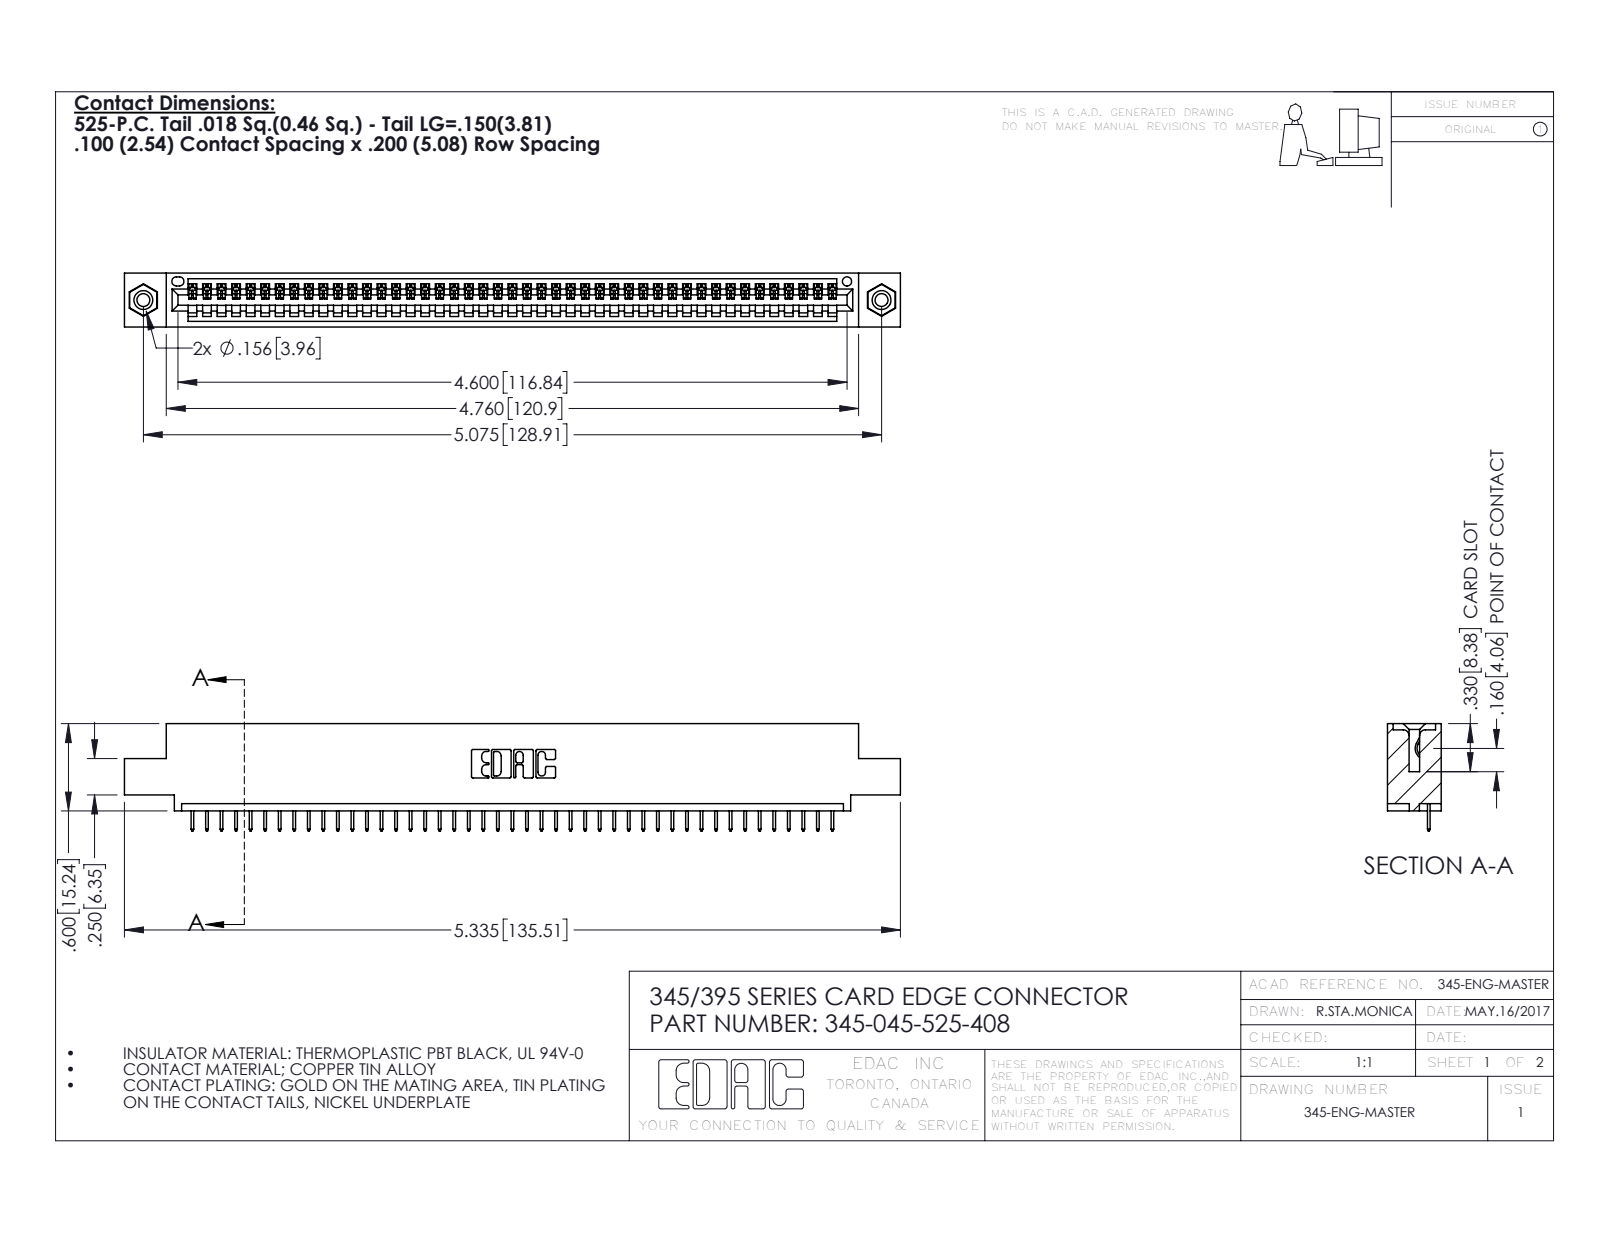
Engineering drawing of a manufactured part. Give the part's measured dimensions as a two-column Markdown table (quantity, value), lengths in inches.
| quantity | value |
| --- | --- |
| part name | 345-250-001_345-250-003-102; 345-292-001_345-293-125; 345 Part_0.110 Offset - 0.156 Dia-TI; 345-045-525-408 |
| STEP written by | SolidWorks 2020 (CONFIG_CONTROL_DESIGN) |
| units | inches |
| bodies | 48 solids, 2980 faces (2186 planar, 778 cylindrical, 16 other) |
| overall size | 5.335 × 0.737 × 0.37 |
| volume | 0.771 in³ |
| surface area | 25.29 in² |
| round holes (diameter × count) | 0.089 × 2, 0.125 × 2, 0.156 × 2, 0.064 × 1 |
| round bosses / shafts (diameter × count) | 0.155 × 2 |
| partial cylindrical surfaces (radius × count) | 0.006 × 90, 0.01 × 22, 0.007 × 6, 0.031 × 6, 0.026 × 3, 0.031 × 2, 0.04 × 2, 0.014 × 1 |
| main face-to-face distances | 0.072, 0.298, 0.37, 0.2, 0.098, 0.272, 0.025, 0.225, 0.072, 0.149 |
| hole center spacings | 0.27, 4.839, 5.075 |
